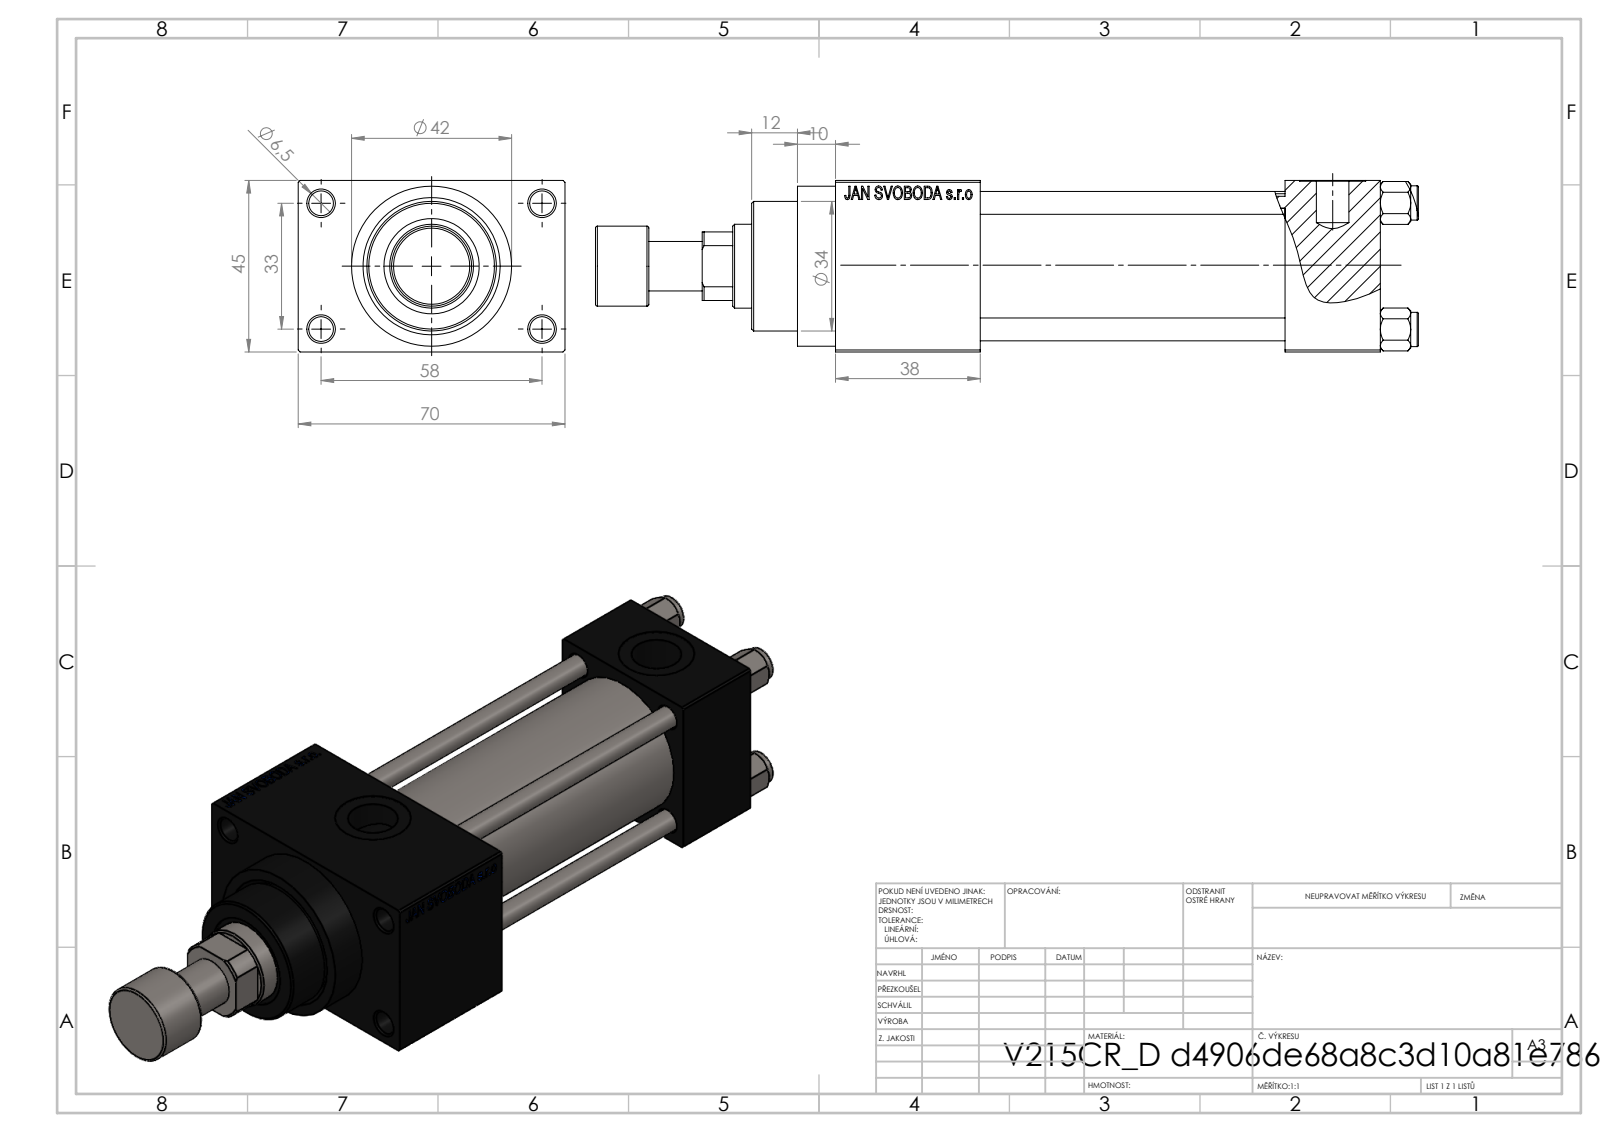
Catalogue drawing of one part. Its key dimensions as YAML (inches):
part_name: "V215_VC_A; V215CR_VCP_D; V215CR_D_TYCINKA; V215CR_D_Body (+2 more)"
step_written_by: "SolidWorks 2019 (CONFIG_CONTROL_DESIGN)"
units: inches
bodies: {solids: 12, faces: 1116, planar: 499, cylindrical: 93, other: 524}
overall_size: [8.504, 2.756, 1.772]
volume: 16.84
surface_area: 143.3
round_holes:
  - {diameter: 0.236, count: 4}
  - {diameter: 0.256, count: 4}
  - {diameter: 0.276, count: 2}
  - {diameter: 0.518, count: 2}
  - {diameter: 0.787, count: 2}
  - {diameter: 0.413, count: 1}
  - {diameter: 0.866, count: 1}
  - {diameter: 0.945, count: 1}
  - {diameter: 0.984, count: 1}
  - {diameter: 1.26, count: 1}
  - {diameter: 1.299, count: 1}
round_bosses_or_shafts:
  - {diameter: 0.354, count: 4}
  - {diameter: 1.654, count: 1}
  - {diameter: 1.496, count: 1}
  - {diameter: 1.339, count: 1}
  - {diameter: 0.827, count: 1}
  - {diameter: 0.512, count: 1}
face_to_face_distances: [1.772, 0.984, 0.492, 2.264, 3.15, 4.134, 4.646, 2.756, 1.496, 5.63]
hole_center_spacings: [0.488, 0.924, 1.307, 1.314, 1.392, 1.795, 2.219, 1.299]
